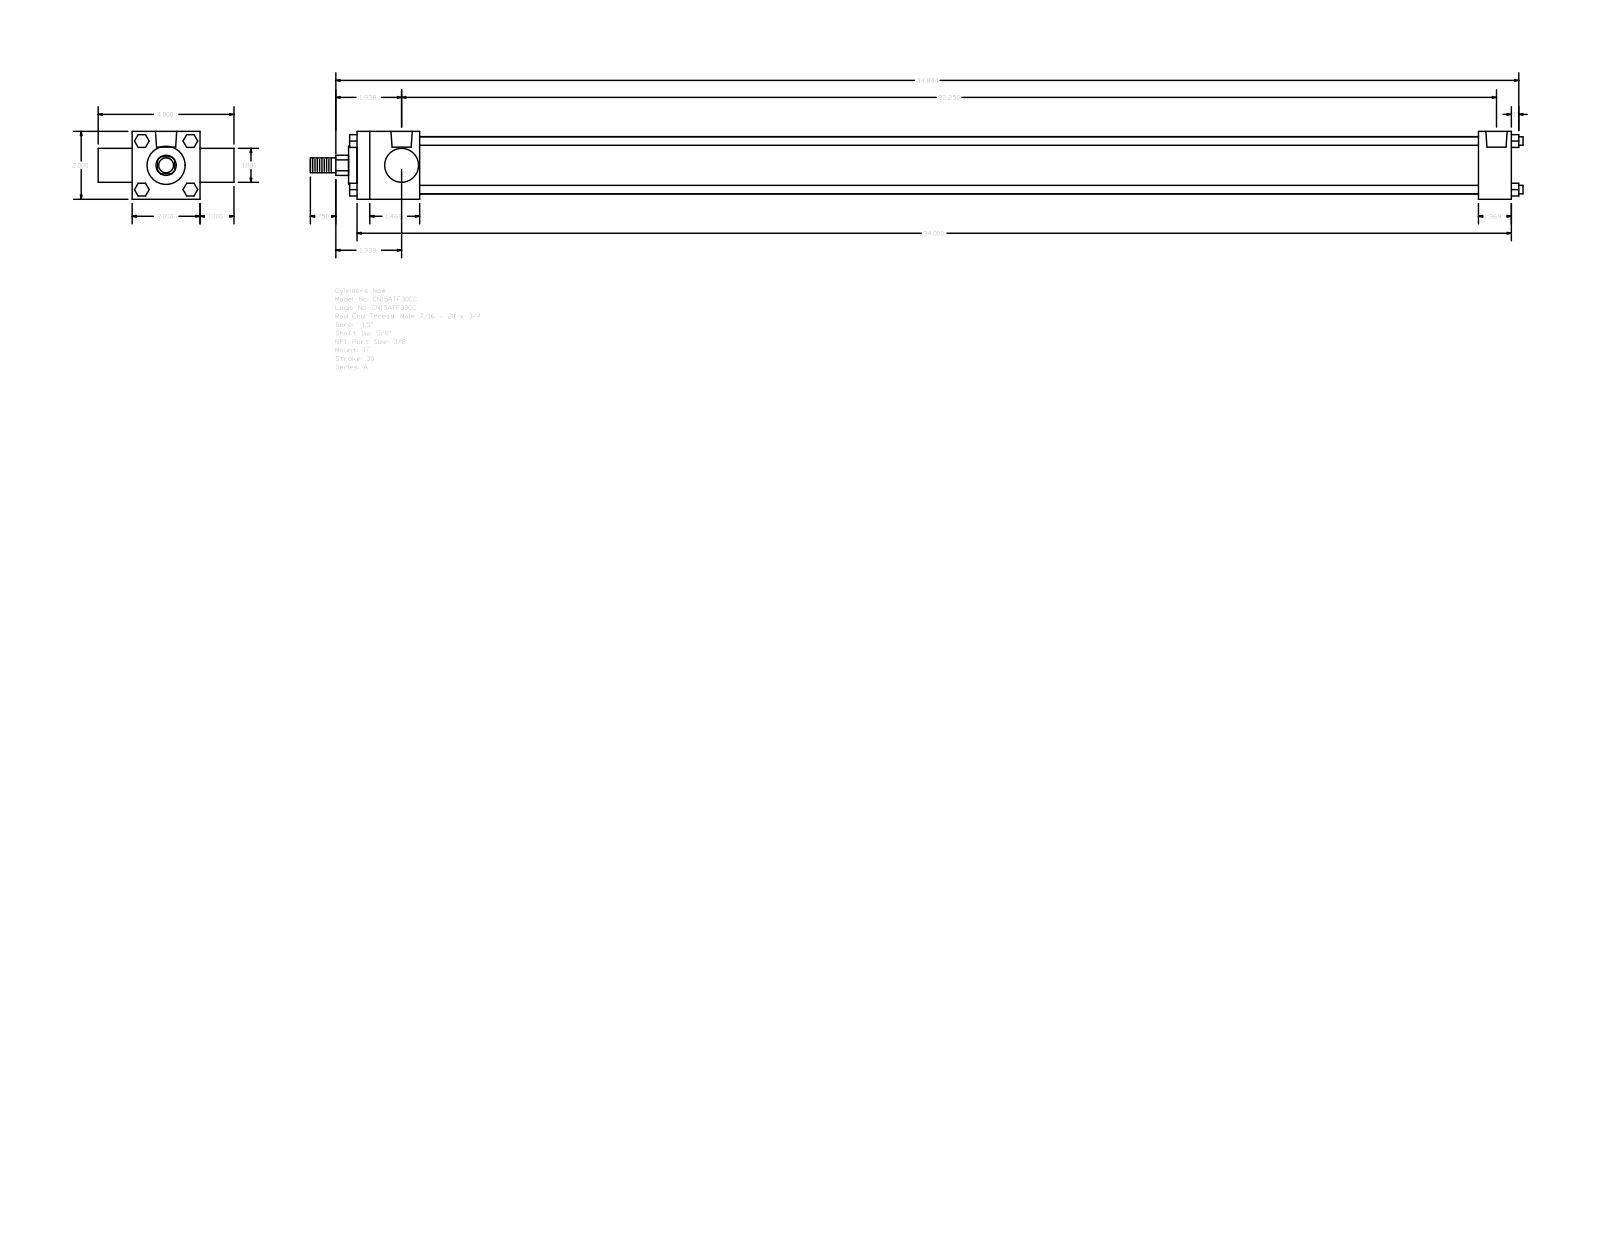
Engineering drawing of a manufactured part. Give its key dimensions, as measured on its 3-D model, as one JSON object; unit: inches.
{"part_name": "A_TF__0150_0.625", "step_written_by": "GSSL Pune (CONFIG_CONTROL_DESIGN)", "units": "inches", "bodies": {"solids": 0, "faces": 120, "planar": 92, "cylindrical": 28, "other": 0}, "overall_size": [35.719, 4, 2], "round_holes": [[0.219, 3], [0.627, 2]], "round_bosses_or_shafts": [[0.25, 4], [1.69, 1], [1.125, 1], [1, 1], [0.625, 1], [0.437, 1]], "partial_cylinders_radius": [[0.297, 1]], "face_to_face_distances": [2, 34, 1, 3, 1.844, 33.031, 31.187, 32.156, 0.969, 4], "hole_center_spacings": [0.156, 32.094, 31.937, 32.25]}
